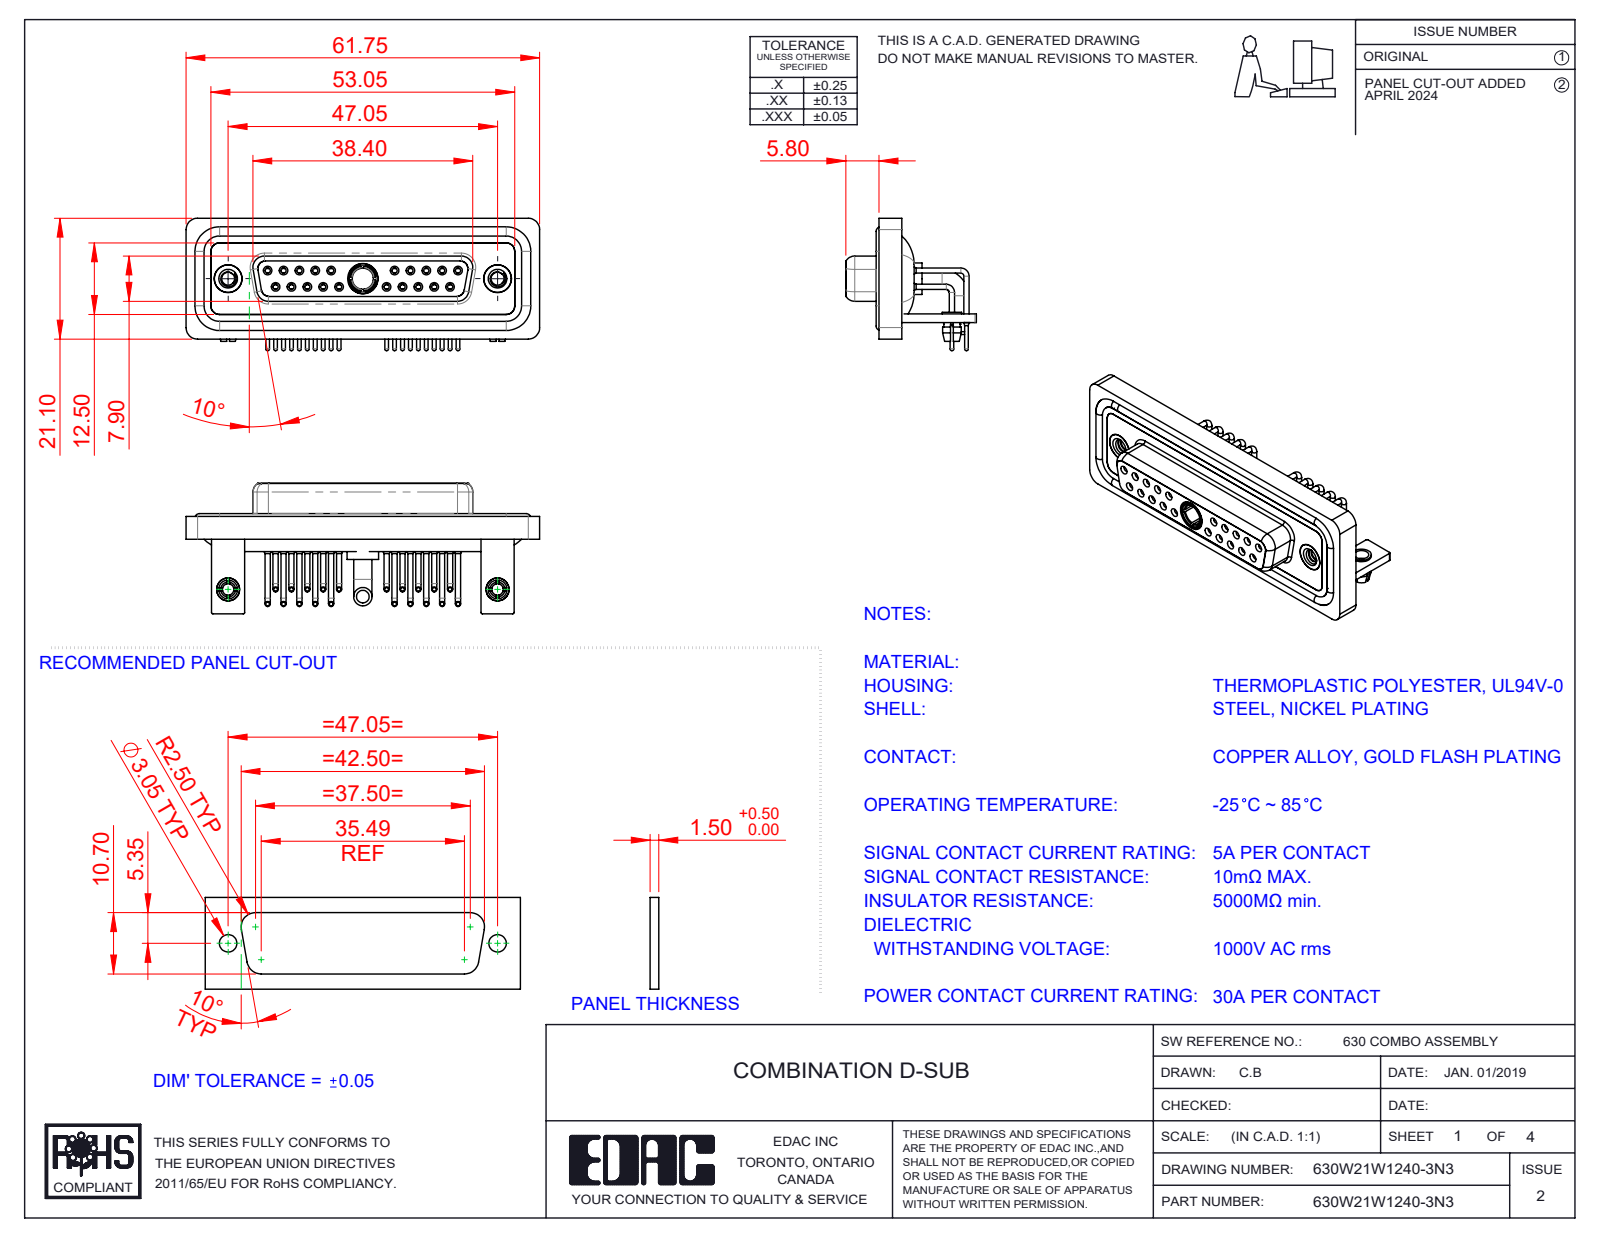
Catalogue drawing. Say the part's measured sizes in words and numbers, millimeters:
The part is named "630Combo Shell Front_25 Contacts; 630Combo Threaded Rivet_2; 630Combo Shell Rear_25 Contacts; 630Combo Stabilizer Bracket_50 Contacts (+7 more)". Its 3-D file was written by "SolidWorks 2023 (CONFIG_CONTROL_DESIGN)". It is 33 solids with 1664 faces: 502 planar, 729 cylindrical and 433 other. Overall it measures 61.75 by 23.12 by 22.8 millimeters. Its volume is 8 936 cubic millimeters and its surface area 15 744 square millimeters. Round holes: 22 of diameter 2, 20 of diameter 0.9, 20 of diameter 1.1, 20 of diameter 1.5, 10 of diameter 1.6, 10 of diameter 1.7, 3 of diameter 4.85, 2 of diameter 2.26, 2 of diameter 2.5, 2 of diameter 3.2, 2 of diameter 4, 2 of diameter 4.05. Round bosses or shafts: 20 of diameter 0.9, 20 of diameter 0.65, 14 of diameter 1.6, 2 of diameter 4.95, 2 of diameter 4.8, 2 of diameter 4, 2 of diameter 3.4, 2 of diameter 3.3. Partial cylindrical surfaces (rounded edges, fillets, slot ends): 19 of radius 2, 18 of radius 1.5, 16 of radius 0.25, 8 of radius 1.35, 8 of radius 1.6, 5 of radius 0.5, 4 of radius 0.6, 4 of radius 0.65. The main face-to-face distances are 0.4, 1.8, 2.9, 3.7, 1.5, 4.1, 1.1, 1.4, 1.6, 2.5. The hole center spacings are 3.16, 2.77, 5.54, 8.31, 5.04, 19.39, 20.97, 22.16.
